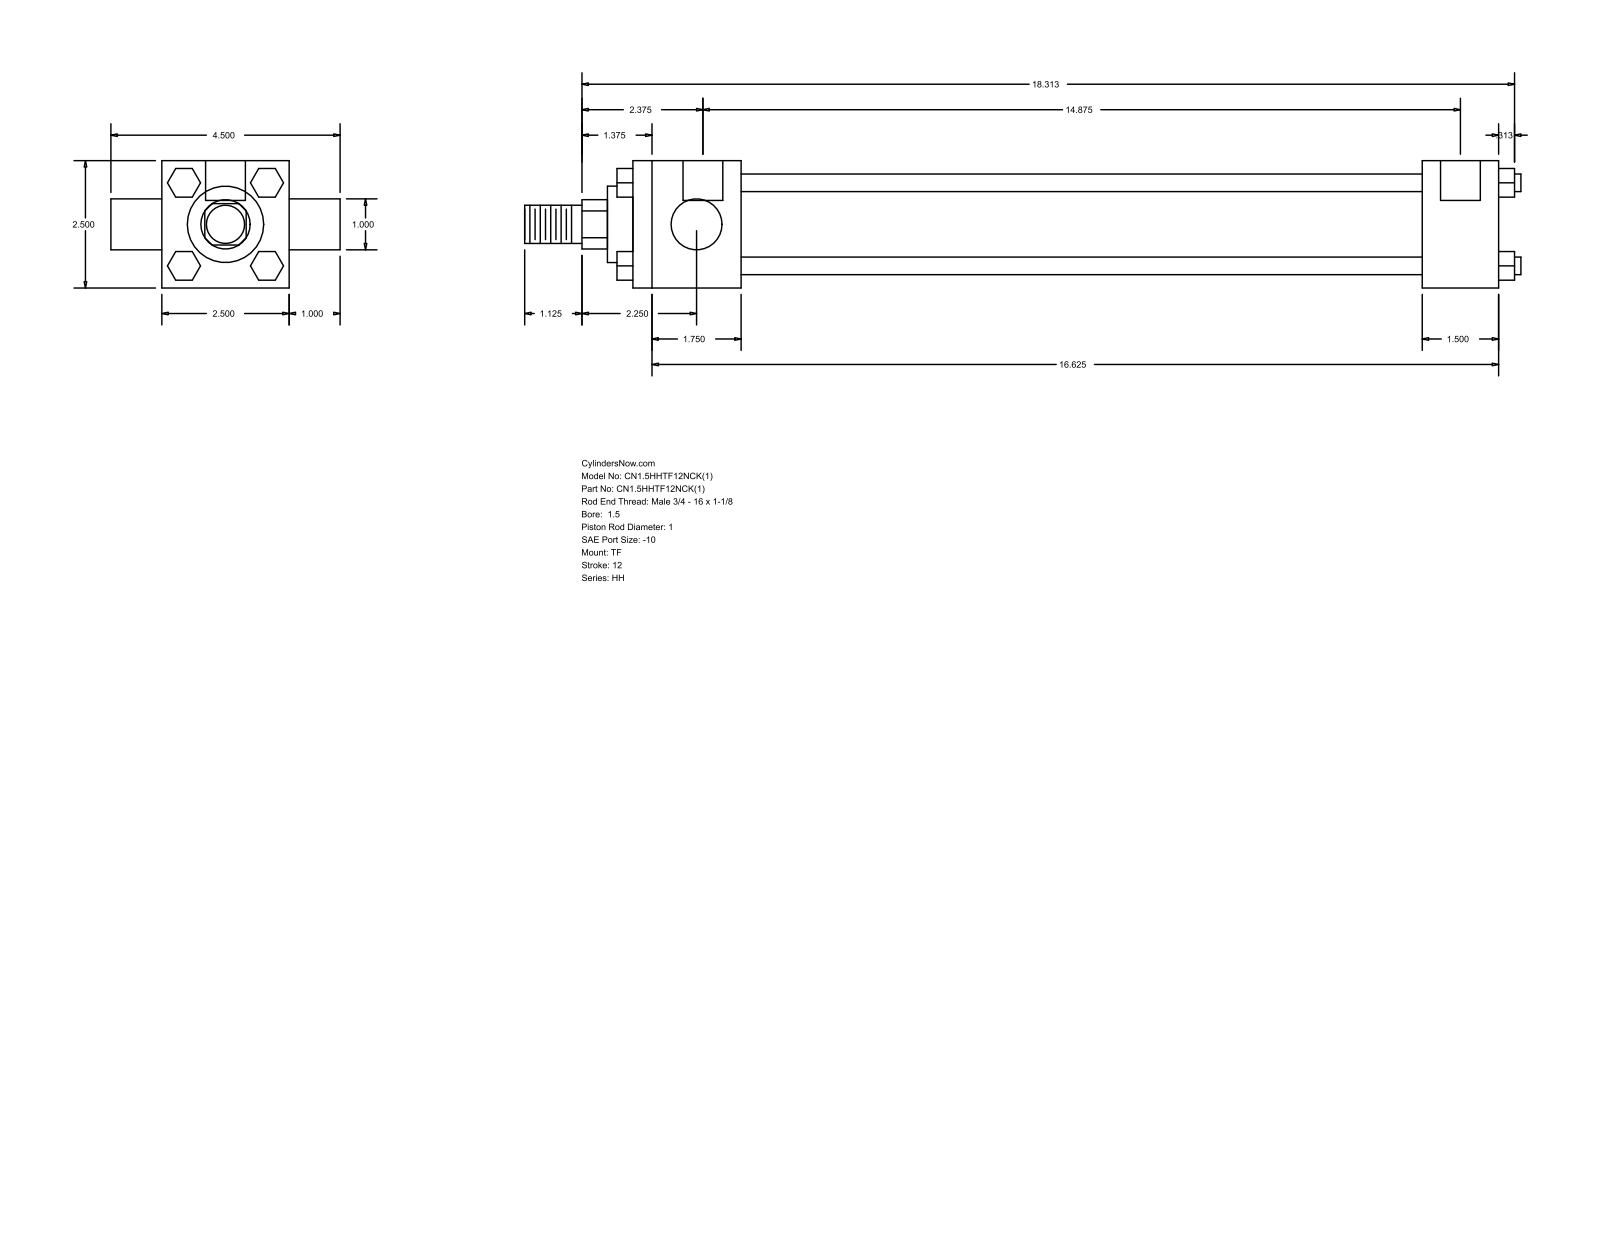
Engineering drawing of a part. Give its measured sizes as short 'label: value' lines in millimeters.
name: HH_TF__0150_1
written by: GSSL Pune (CONFIG_CONTROL_DESIGN)
unit: mm
bodies: 0 solids, 120 faces (92 planar, 28 cylindrical, 0 other)
size: 496.89 × 114.3 × 63.5
holes: 3× ⌀5.56, 2× ⌀19.84
bosses: 4× ⌀8.76, 2× ⌀25.4, 1× ⌀44.45, 1× ⌀38.1, 1× ⌀19.05
rounds: 1× R12.29
face distances: 63.5, 38.1, 377.82, 339.72, 53.98, 393.7, 431.8, 25.4, 20.7, 14.29
hole spacings: 1.59, 379.41, 377.82, 381
